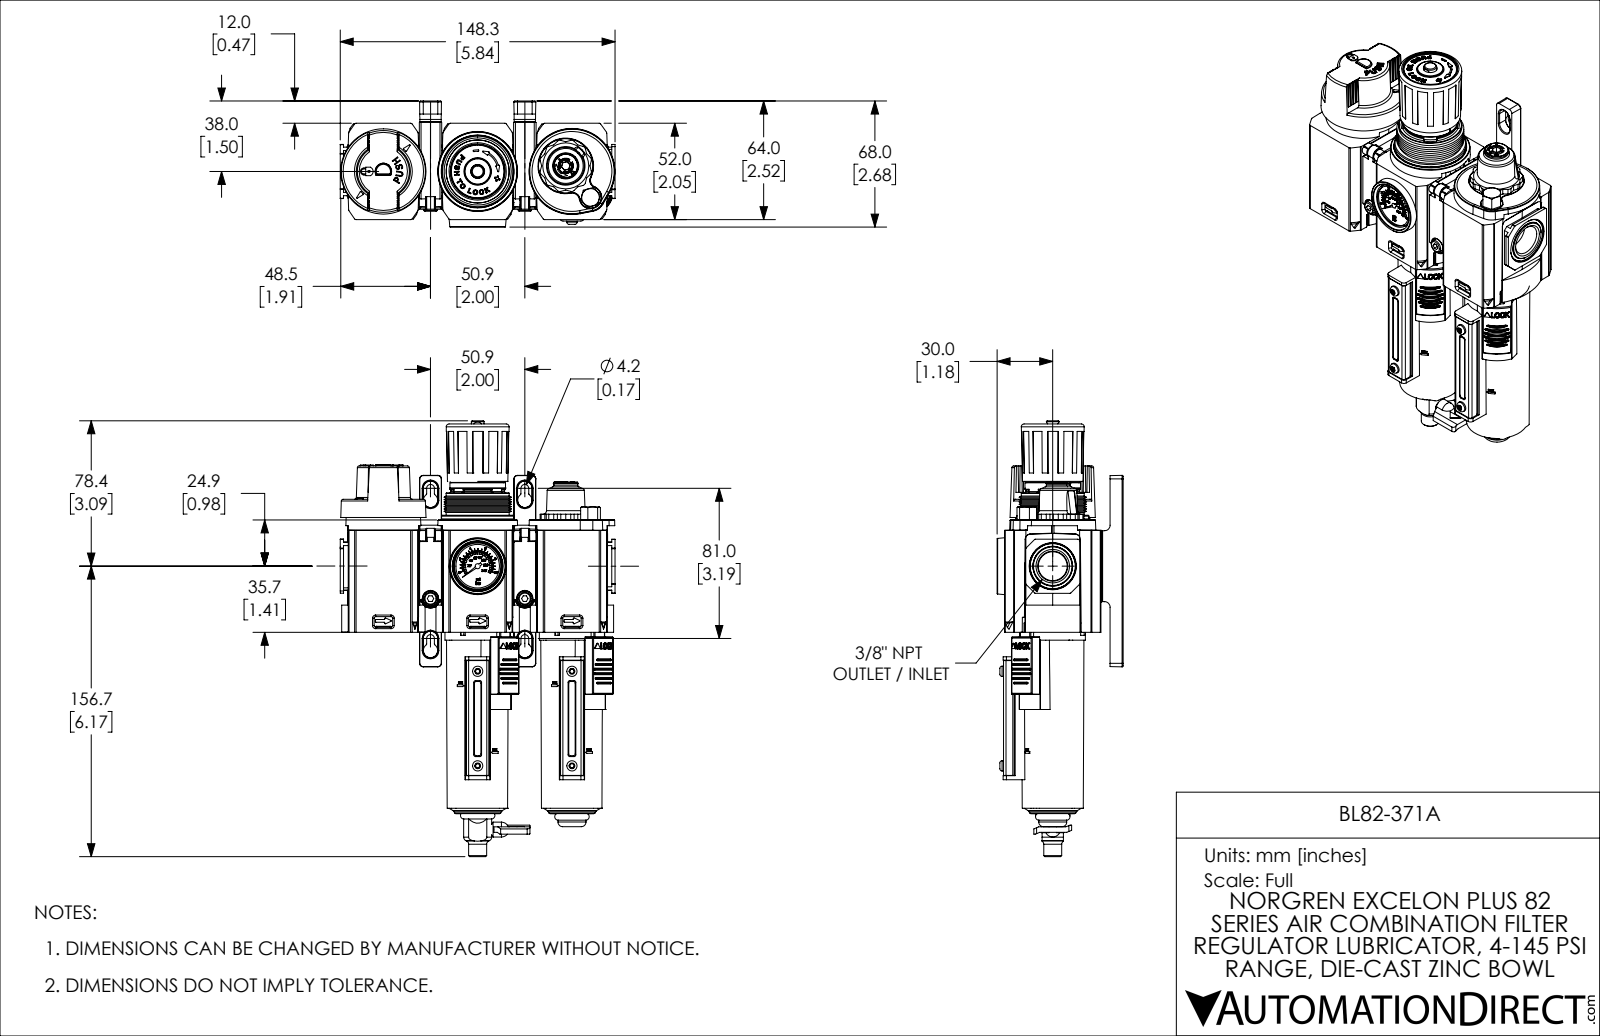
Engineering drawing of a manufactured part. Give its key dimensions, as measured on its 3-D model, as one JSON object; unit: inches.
{"part_name": "BL82-371A", "step_written_by": "SolidWorks 2021 (CONFIG_CONTROL_DESIGN)", "units": "inches", "bodies": {"solids": 20, "faces": 5440, "planar": 2310, "cylindrical": 2179, "other": 951}, "overall_size": [9.257, 5.839, 2.676], "volume_in3": 37.57, "surface_area_in2": 330.2, "round_holes": [[0.097, 4], [0.306, 4], [0.039, 2], [0.128, 2], [0.138, 2], [0.175, 2], [0.187, 2], [0.628, 2], [0.106, 1], [0.128, 1], [0.197, 1], [0.199, 1]], "round_bosses_or_shafts": [[0.276, 4], [0.217, 4], [1.388, 2], [1.356, 2], [1.291, 2], [1.257, 2], [0.906, 2], [0.626, 2]], "partial_cylinders_radius": [[0.039, 152], [0.02, 148], [0.01, 27], [0.006, 26], [0.009, 25], [0.011, 25], [0.012, 25], [0.03, 25]], "face_to_face_distances": [0.059, 2.004, 1.988, 2.002, 2.047, 1.929, 4.004, 1.352, 0.182, 0.152], "hole_center_spacings": [0.63, 2.004, 0.554, 1.58, 0.59, 0.689, 1.002, 1.091]}
